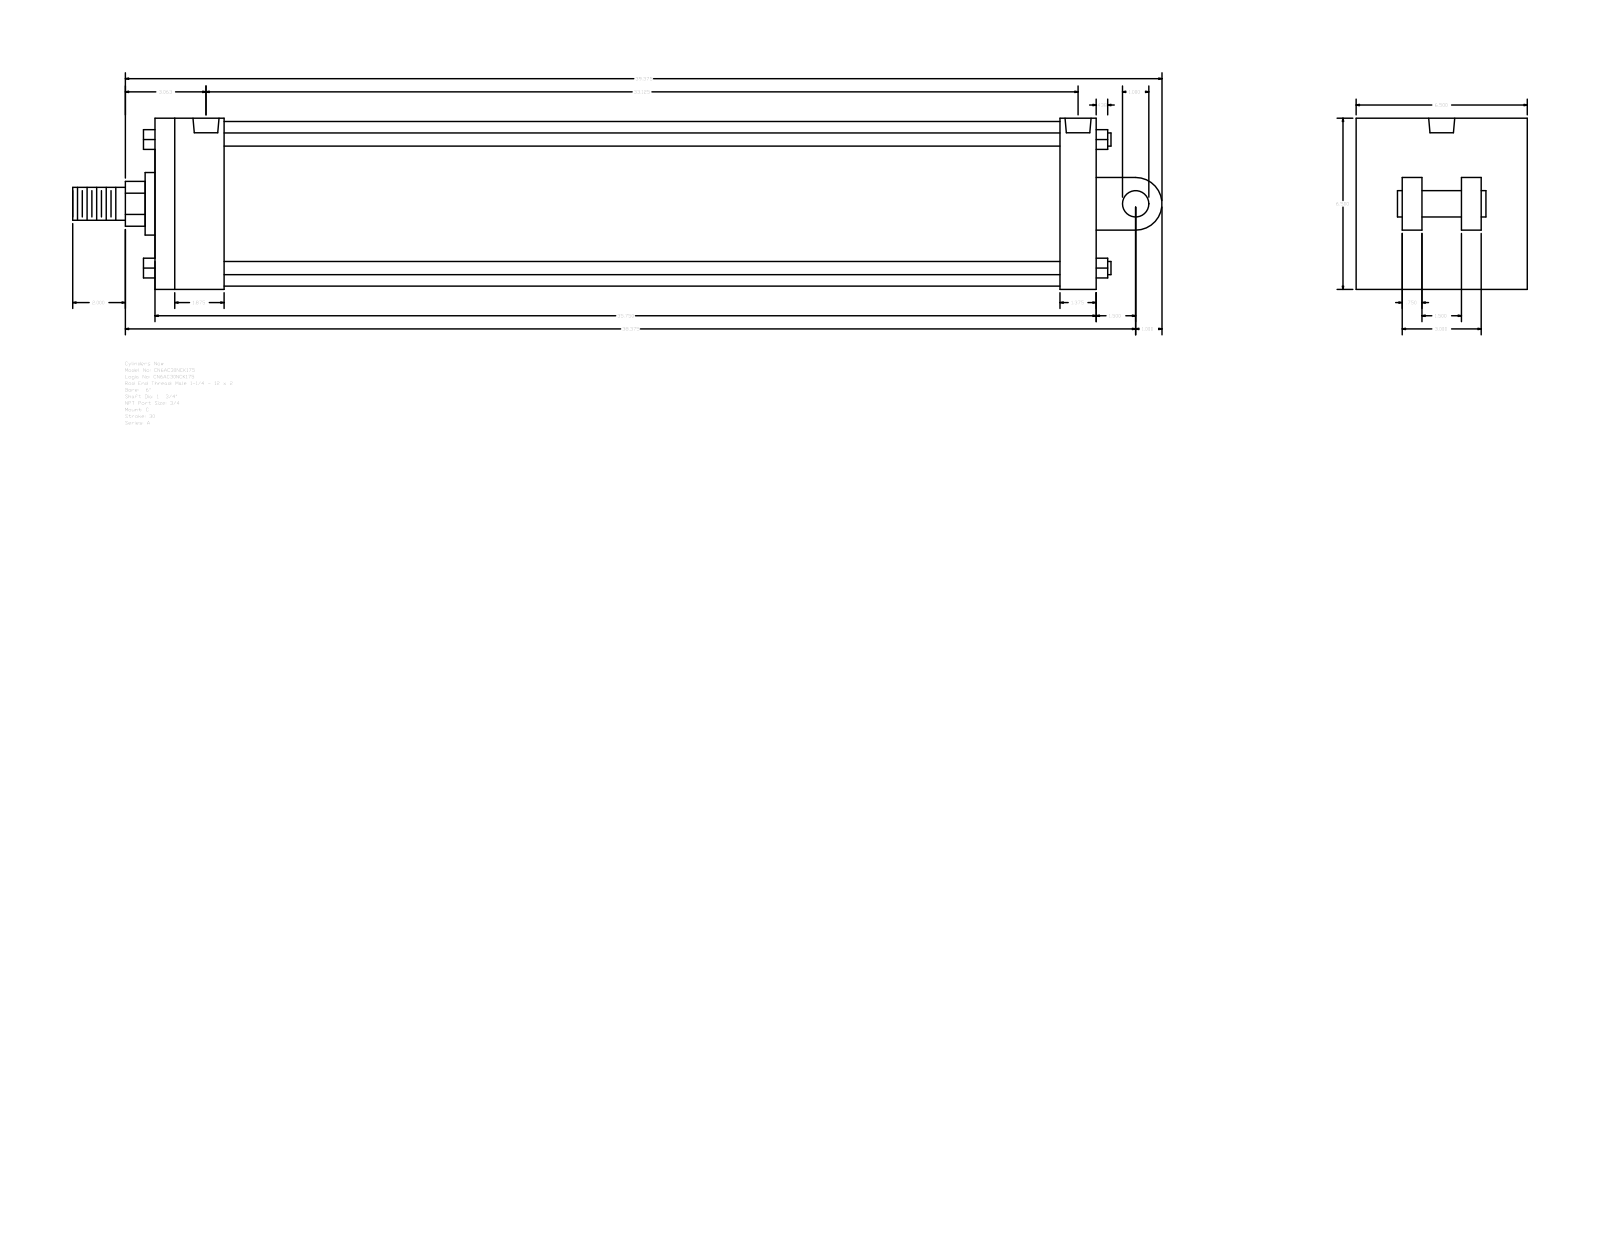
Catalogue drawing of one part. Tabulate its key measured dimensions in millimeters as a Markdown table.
| quantity | value |
| --- | --- |
| part name | A_C__0600_1.75 |
| STEP written by | GSSL Pune (CONFIG_CONTROL_DESIGN) |
| units | millimeters |
| bodies | 0 solids, 135 faces (102 planar, 33 cylindrical, 0 other) |
| overall size | 1050.92 × 165.1 × 165.1 |
| round holes (diameter × count) | 15.08 × 4, 25.12 × 2 |
| round bosses / shafts (diameter × count) | 12.7 × 4, 158.75 × 1, 60.33 × 1, 44.45 × 1, 31.75 × 1, 25.4 × 1 |
| partial cylindrical surfaces (radius × count) | 21.63 × 1, 25.4 × 1 |
| main face-to-face distances | 165.1, 908.05, 19.05, 57.15, 66.68, 841.37, 873.13, 806.45, 34.92, 63.5 |
| hole center spacings | 5.56, 830.25, 835.81, 841.37 |
